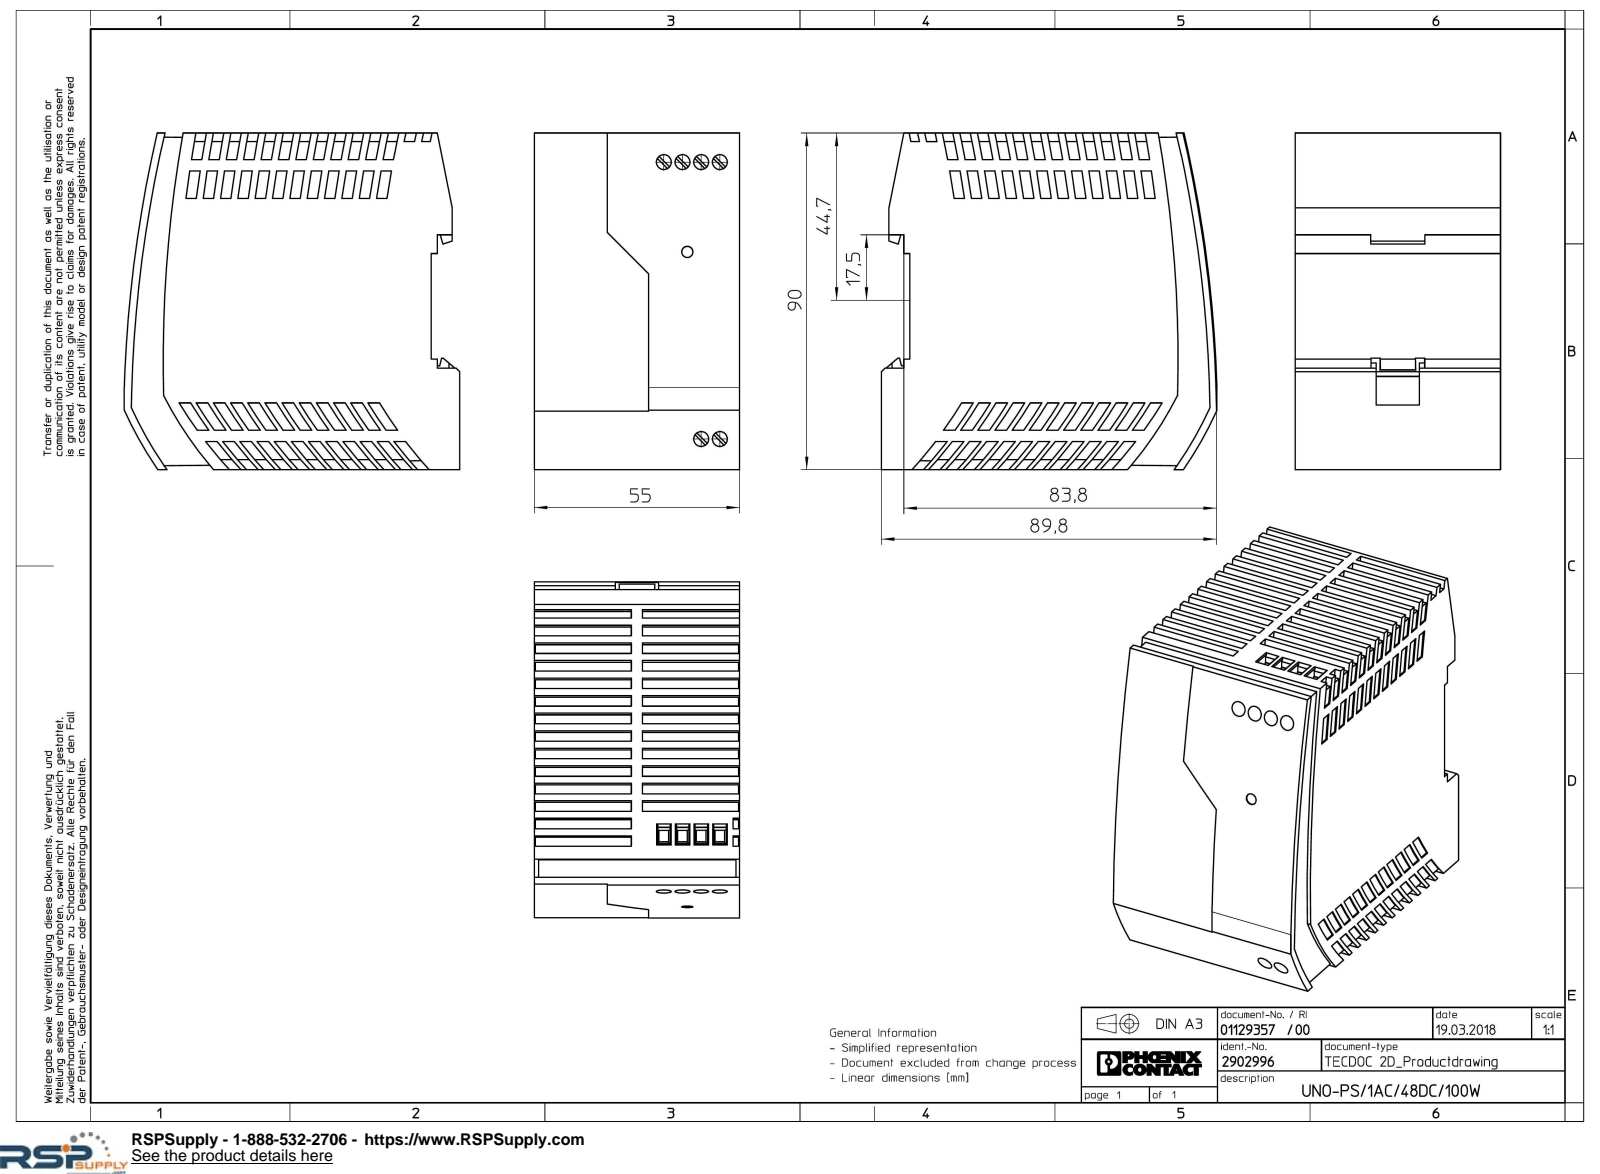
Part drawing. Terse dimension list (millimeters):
name: UNO_PS_1AC_48DC_100W-select
written by: Creo Elements/Direct Modeling 18.1I 14-Aug-2016 (C) Parametric Technology GmbH (AUTOMOTIVE_DESIGN)
unit: mm
bodies: 1 solid, 779 faces (558 planar, 219 cylindrical, 2 other)
size: 90 × 89.87 × 55
volume: 395 571 mm³; area: 43 992 mm²
holes: 6× ⌀4
rounds: 26× R111, 1× R98, 1× R98.55, 1× R100, 1× R282.66, 1× R284.9, 1× R286.76, 1× R291.36
face distances: 55, 2.3, 87.7, 90, 2.7, 85, 87.3, 54.7, 7.6, 54.4
hole spacings: 5, 74.17, 10, 74, 74.67, 15, 75.5
